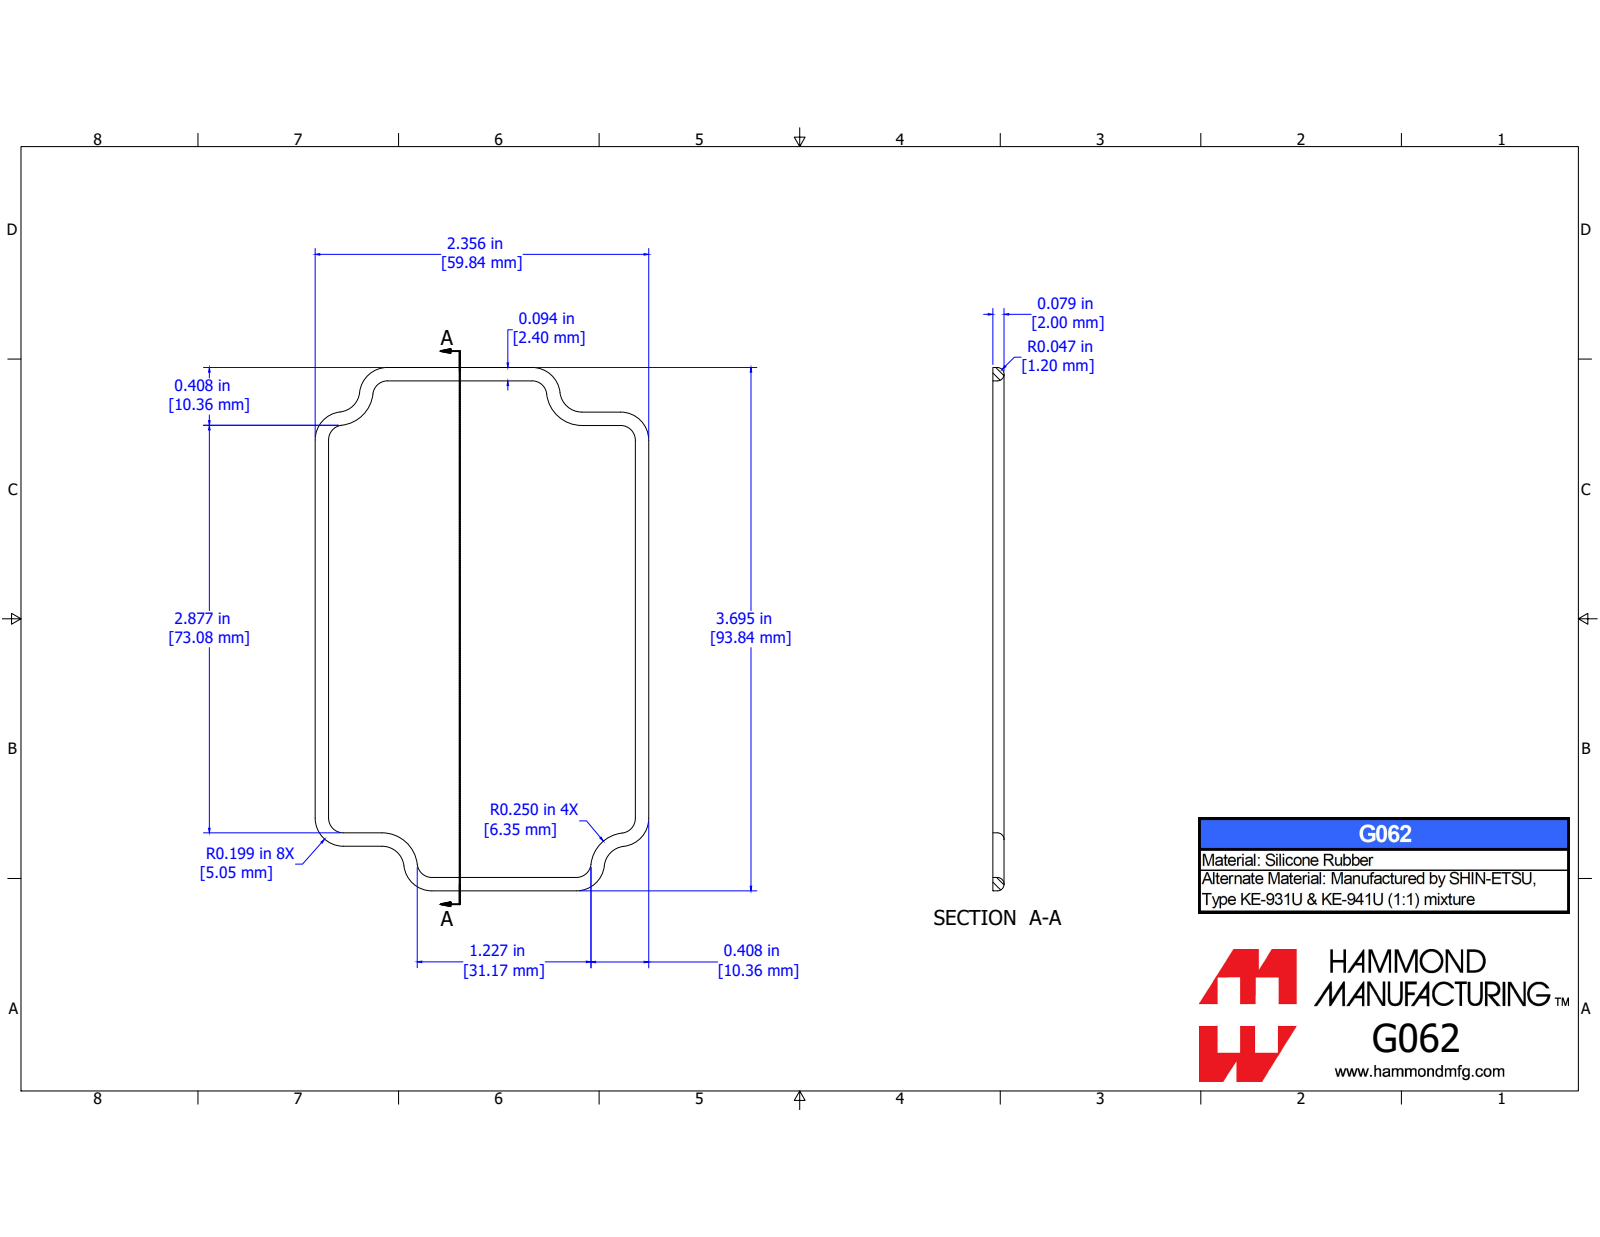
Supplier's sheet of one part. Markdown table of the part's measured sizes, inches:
| quantity | value |
| --- | --- |
| part name | 1590Z062G |
| STEP written by | SolidWorks 2019 (CONFIG_CONTROL_DESIGN) |
| units | inches |
| bodies | 1 solid, 158 faces (40 planar, 24 cylindrical, 94 other) |
| overall size | 3.768 × 2.429 × 0.093 |
| volume | 0.083 in³ |
| surface area | 3.705 in² |
| partial cylindrical surfaces (radius × count) | 0.039 × 20 |
| main face-to-face distances | 2.326, 3.659, 0.345, 3.313, 0.091, 2.968, 1.98, 0.659, 1.667, 0.314 |
